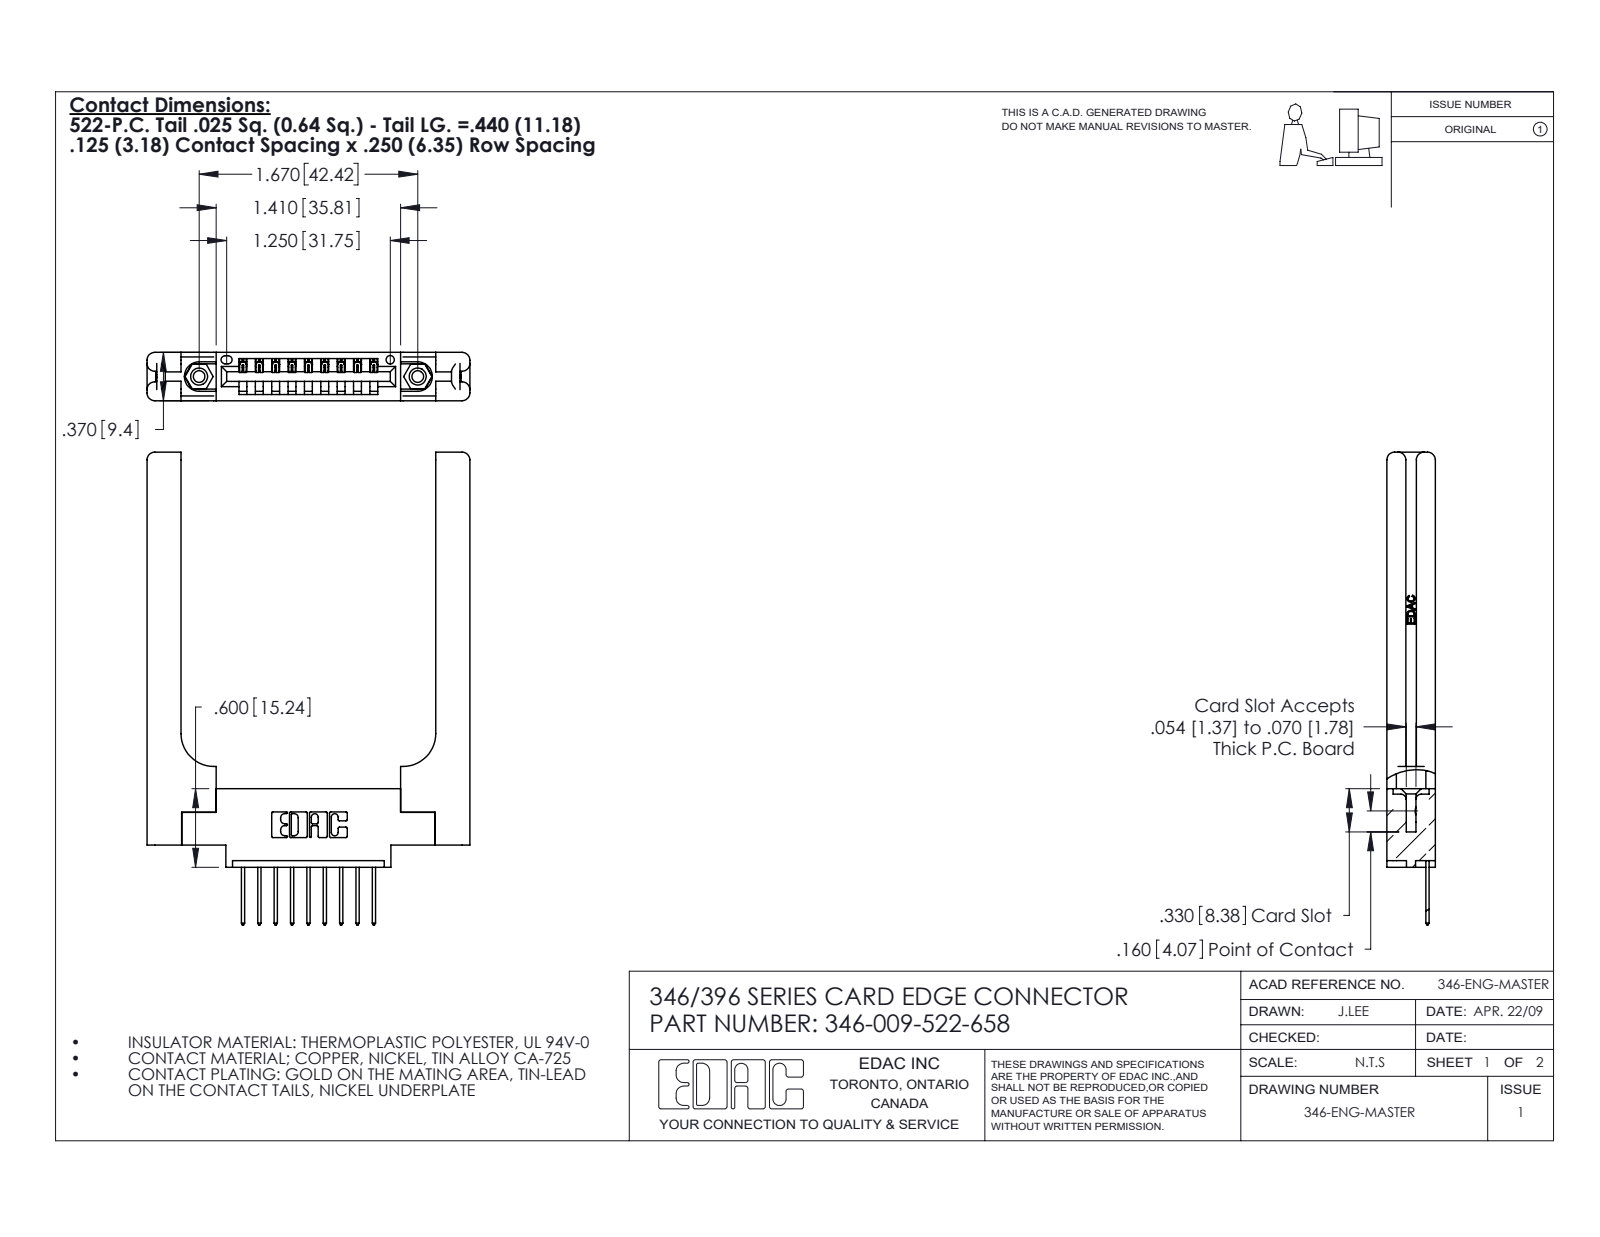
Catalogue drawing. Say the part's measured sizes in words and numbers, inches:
The part is named "345-250-001_345-250-001-102; 346-220-058_345-220-058; 346-009-522-658; 345-292-001_345-293-122 (+1 more)". Its 3-D file was written by "SolidWorks 2020 (CONFIG_CONTROL_DESIGN)". It is 14 solids with 918 faces: 602 planar, 256 cylindrical and 60 other. Overall it measures 3.61 by 2.466 by 0.37 inches. Its volume is 0.8 cubic inches and its surface area 18.65 square inches. Round holes: 2 of diameter 0.089, 2 of diameter 0.125, 2 of diameter 0.156, 1 of diameter 0.064. Round bosses or shafts: 2 of diameter 0.155. Partial cylindrical surfaces (rounded edges, fillets, slot ends): 22 of radius 0.01, 18 of radius 0.006, 18 of radius 0.01, 16 of radius 0.06, 6 of radius 0.007, 6 of radius 0.031, 3 of radius 0.026, 2 of radius 0.03. The main face-to-face distances are 0.37, 0.15, 0.072, 0.22, 0.148, 0.048, 0.322, 0.102, 0.173, 0.25. The hole center spacings are 0.246, 1.465, 1.67.
